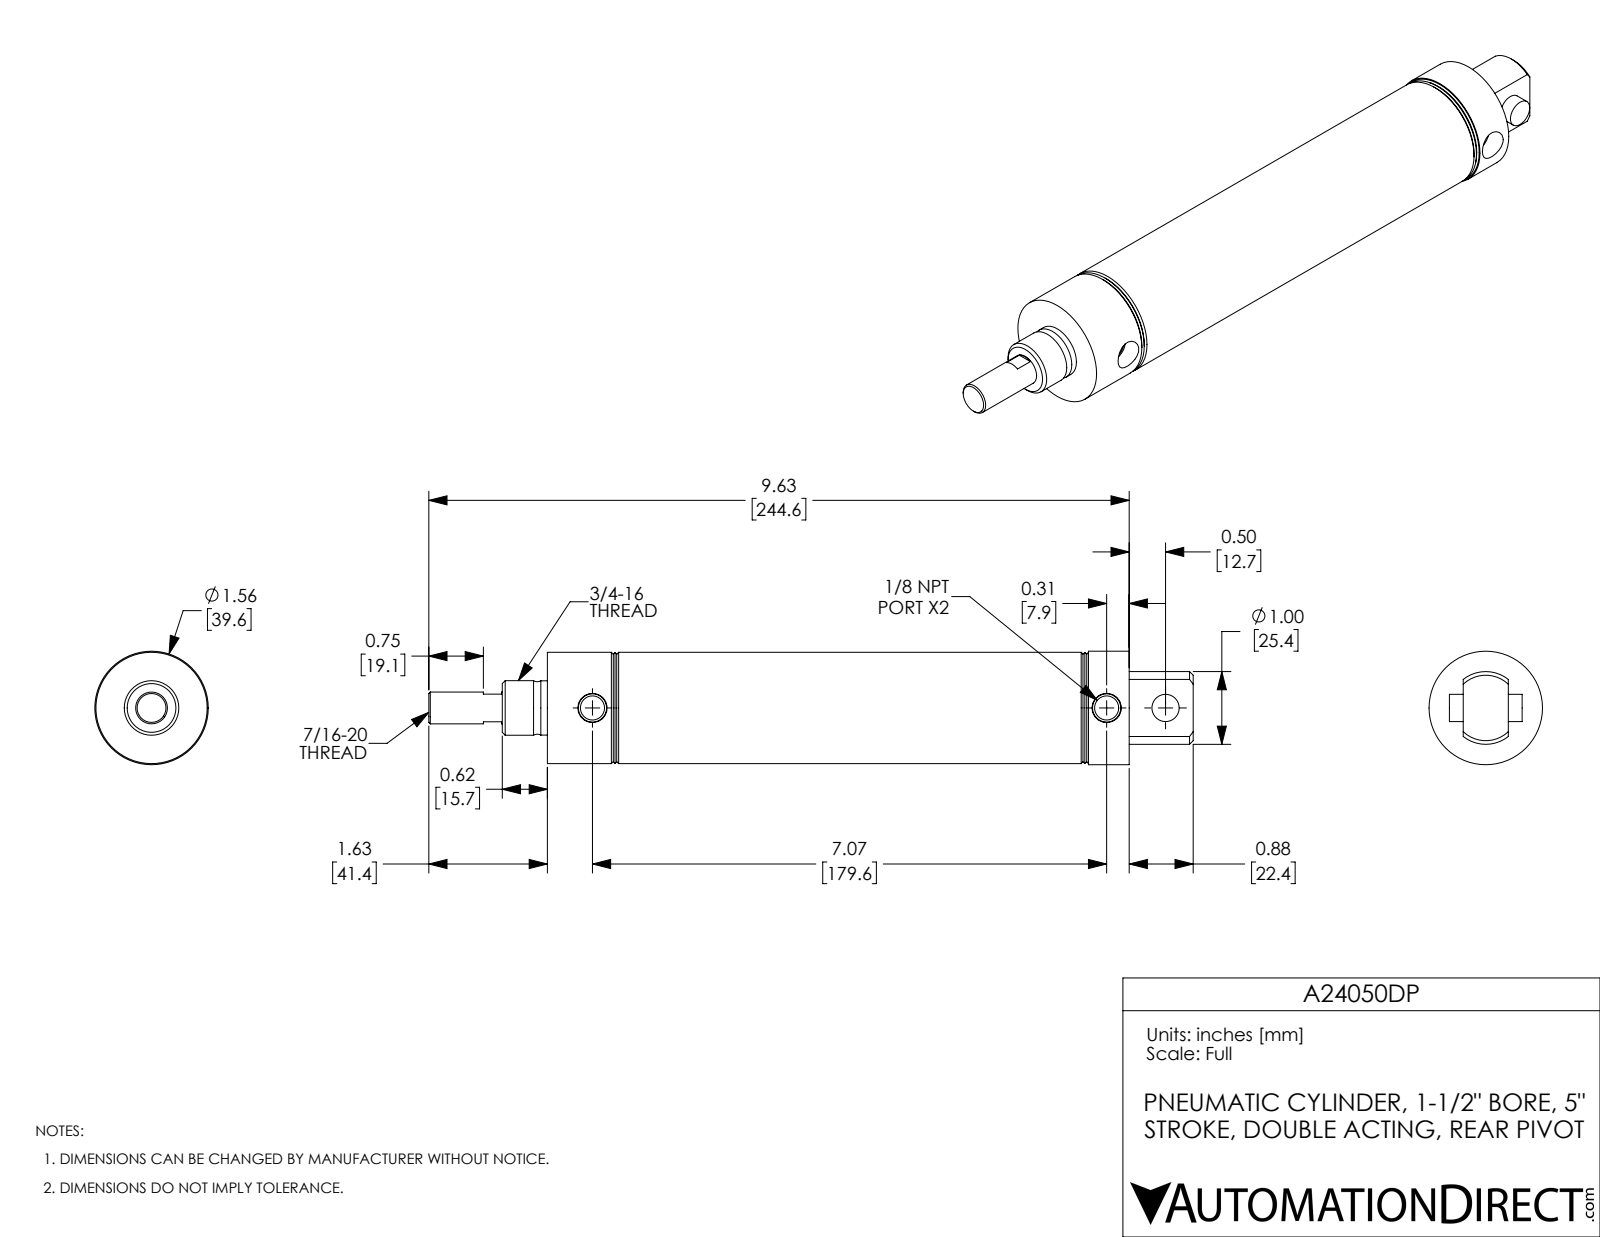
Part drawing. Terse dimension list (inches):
name: A24050DP; A24050DP-MainBody; A24050DP-Rod; A24050DP-Pin
written by: SolidWorks 2017 (AUTOMOTIVE_DESIGN)
unit: in
bodies: 3 solids, 84 faces (22 planar, 28 cylindrical, 34 other)
size: 10.51 × 1.56 × 1.56
volume: 7.516 in³; area: 97.95 in²
holes: 2× ⌀0.332, 1× ⌀0.375, 1× ⌀0.437, 1× ⌀1.5
bosses: 1× ⌀1.56, 1× ⌀1.53, 1× ⌀0.75, 1× ⌀0.746
rounds: 1× R0.5
face distances: 1.25, 6.75, 0.5, 5.5, 5, 6.25, 1.75, 8, 0.62, 0.88
hole spacings: 0.81, 7.07, 7.88
